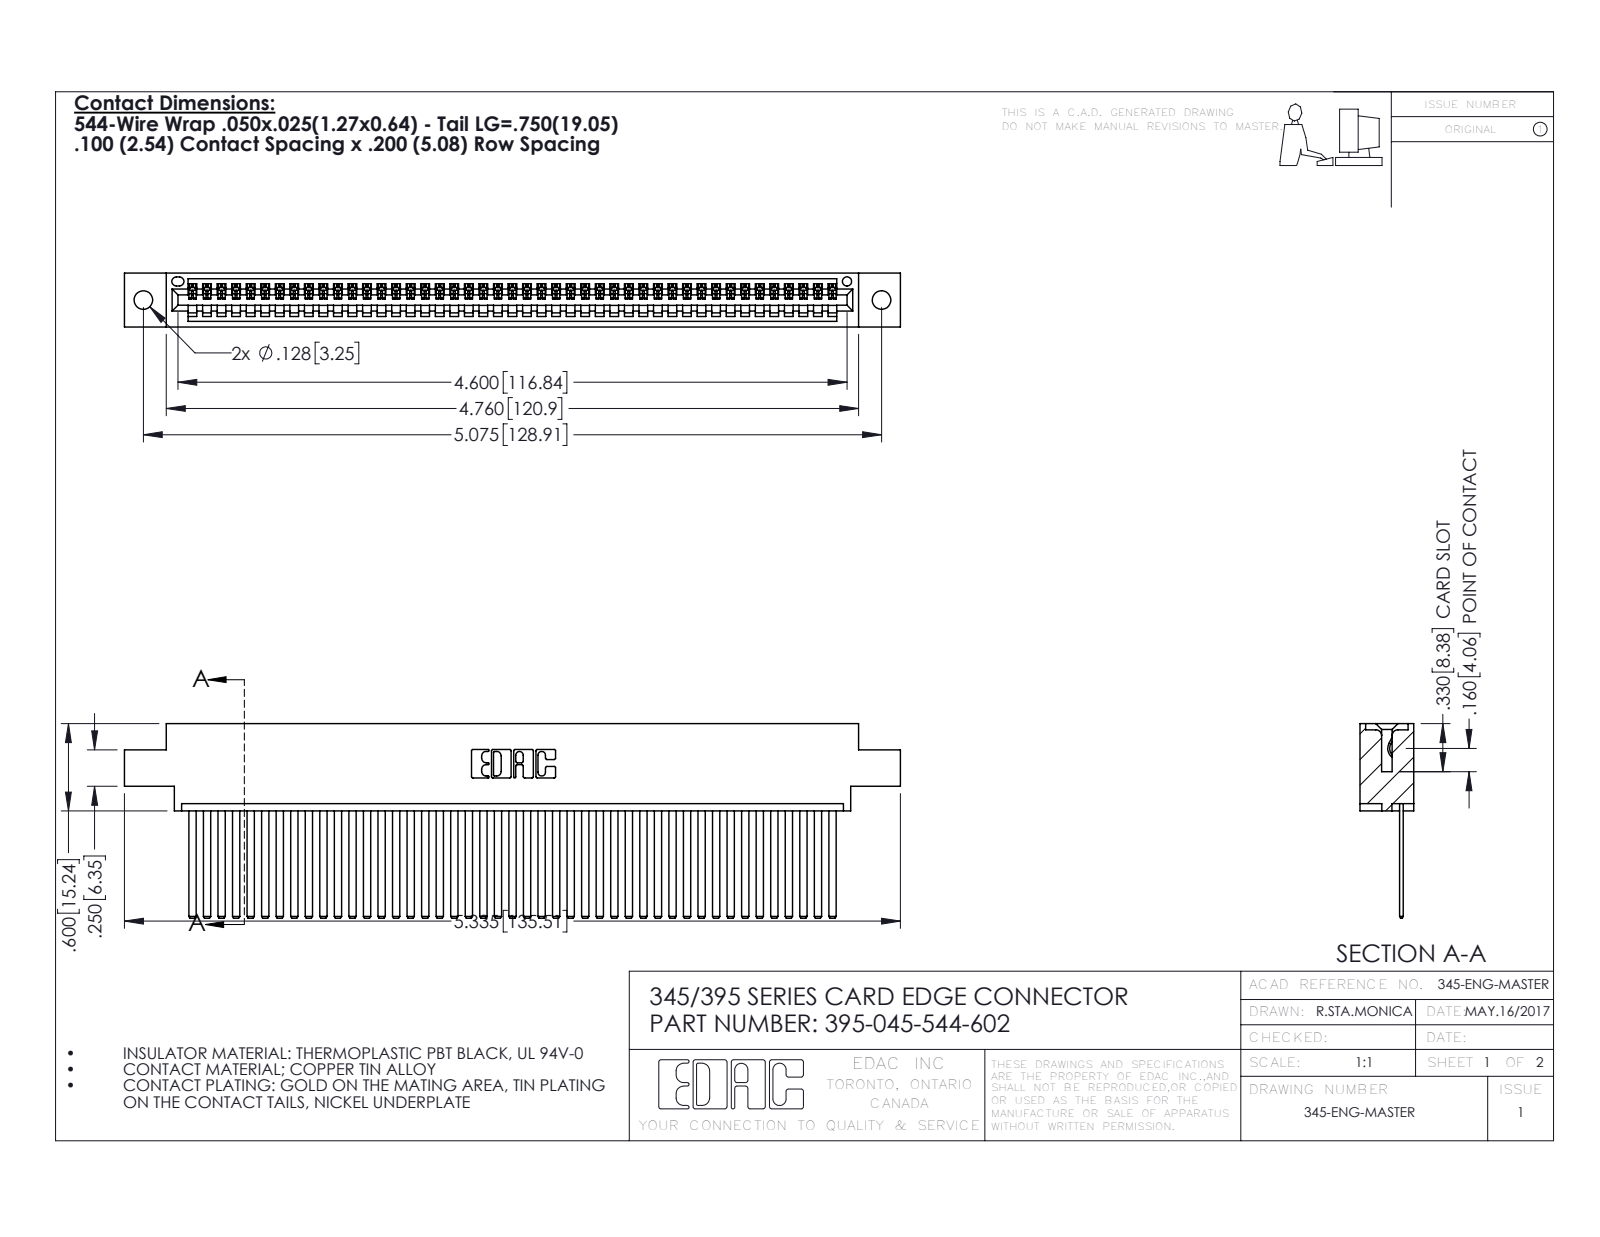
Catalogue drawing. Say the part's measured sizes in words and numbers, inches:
The part is named "345 Part_0.170 Offset - 0.128 Dia; 395-045-544-602; 345-292-001_345-293-144". Its 3-D file was written by "SolidWorks 2016 (CONFIG_CONTROL_DESIGN)". It is 46 solids with 2470 faces: 1704 planar, 766 cylindrical and 0 other. Overall it measures 5.335 by 1.337 by 0.37 inches. Its volume is 0.81 cubic inches and its surface area 29.59 square inches. Round holes: 2 of diameter 0.128, 1 of diameter 0.064. Partial cylindrical surfaces (rounded edges, fillets, slot ends): 90 of radius 0.006, 22 of radius 0.01, 6 of radius 0.007, 6 of radius 0.031, 3 of radius 0.026, 2 of radius 0.031, 2 of radius 0.04, 1 of radius 0.014. The main face-to-face distances are 0.072, 0.298, 0.025, 0.098, 0.272, 0.37, 0.2, 0.225, 0.175, 0.149. The hole center spacings are 0.27, 4.839, 5.075.
